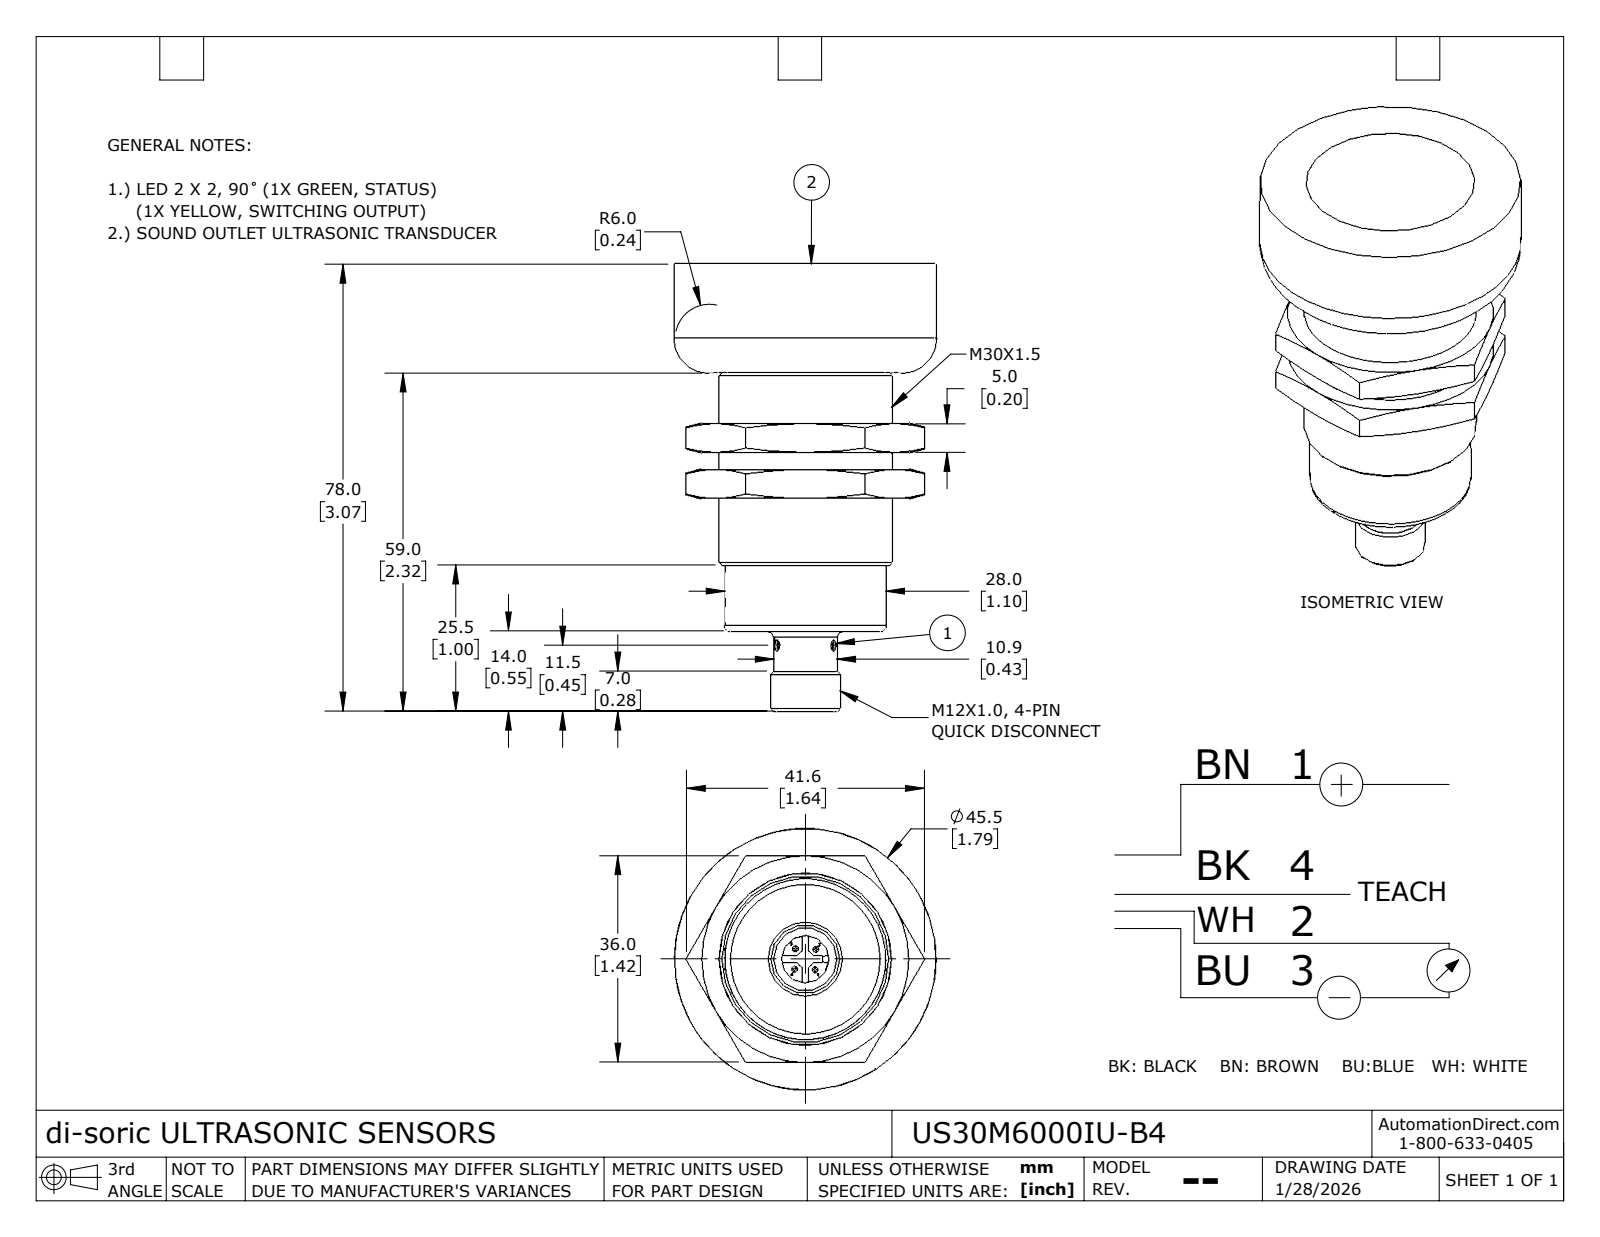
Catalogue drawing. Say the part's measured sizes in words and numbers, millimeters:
The part is named "US30M6000G3-B4". Its 3-D file was written by "SolidWorks 2024 (AUTOMOTIVE_DESIGN)". It is 3 solids with 448 faces: 341 planar, 56 cylindrical and 51 other. Overall it measures 78 by 45.5 by 45.5 millimeters. Its volume is 66 190 cubic millimeters and its surface area 14 767 square millimeters. Round holes: 4 of diameter 1.05, 3 of diameter 2, 1 of diameter 3, 1 of diameter 7.8, 1 of diameter 8.3, 1 of diameter 28.38, 1 of diameter 29.5. Round bosses or shafts: 4 of diameter 1.5, 4 of diameter 1, 1 of diameter 45.5, 1 of diameter 30, 1 of diameter 28, 1 of diameter 12, 1 of diameter 10.9, 1 of diameter 9.8. Partial cylindrical surfaces (rounded edges, fillets, slot ends): 2 of radius 0.5, 1 of radius 0.6, 1 of radius 13.8. The main face-to-face distances are 5, 8, 36, 63.99, 64, 31.14, 32.85, 32.86, 23.14, 40.85. The hole center spacings are 2.5, 3.53, 3.54, 5.
